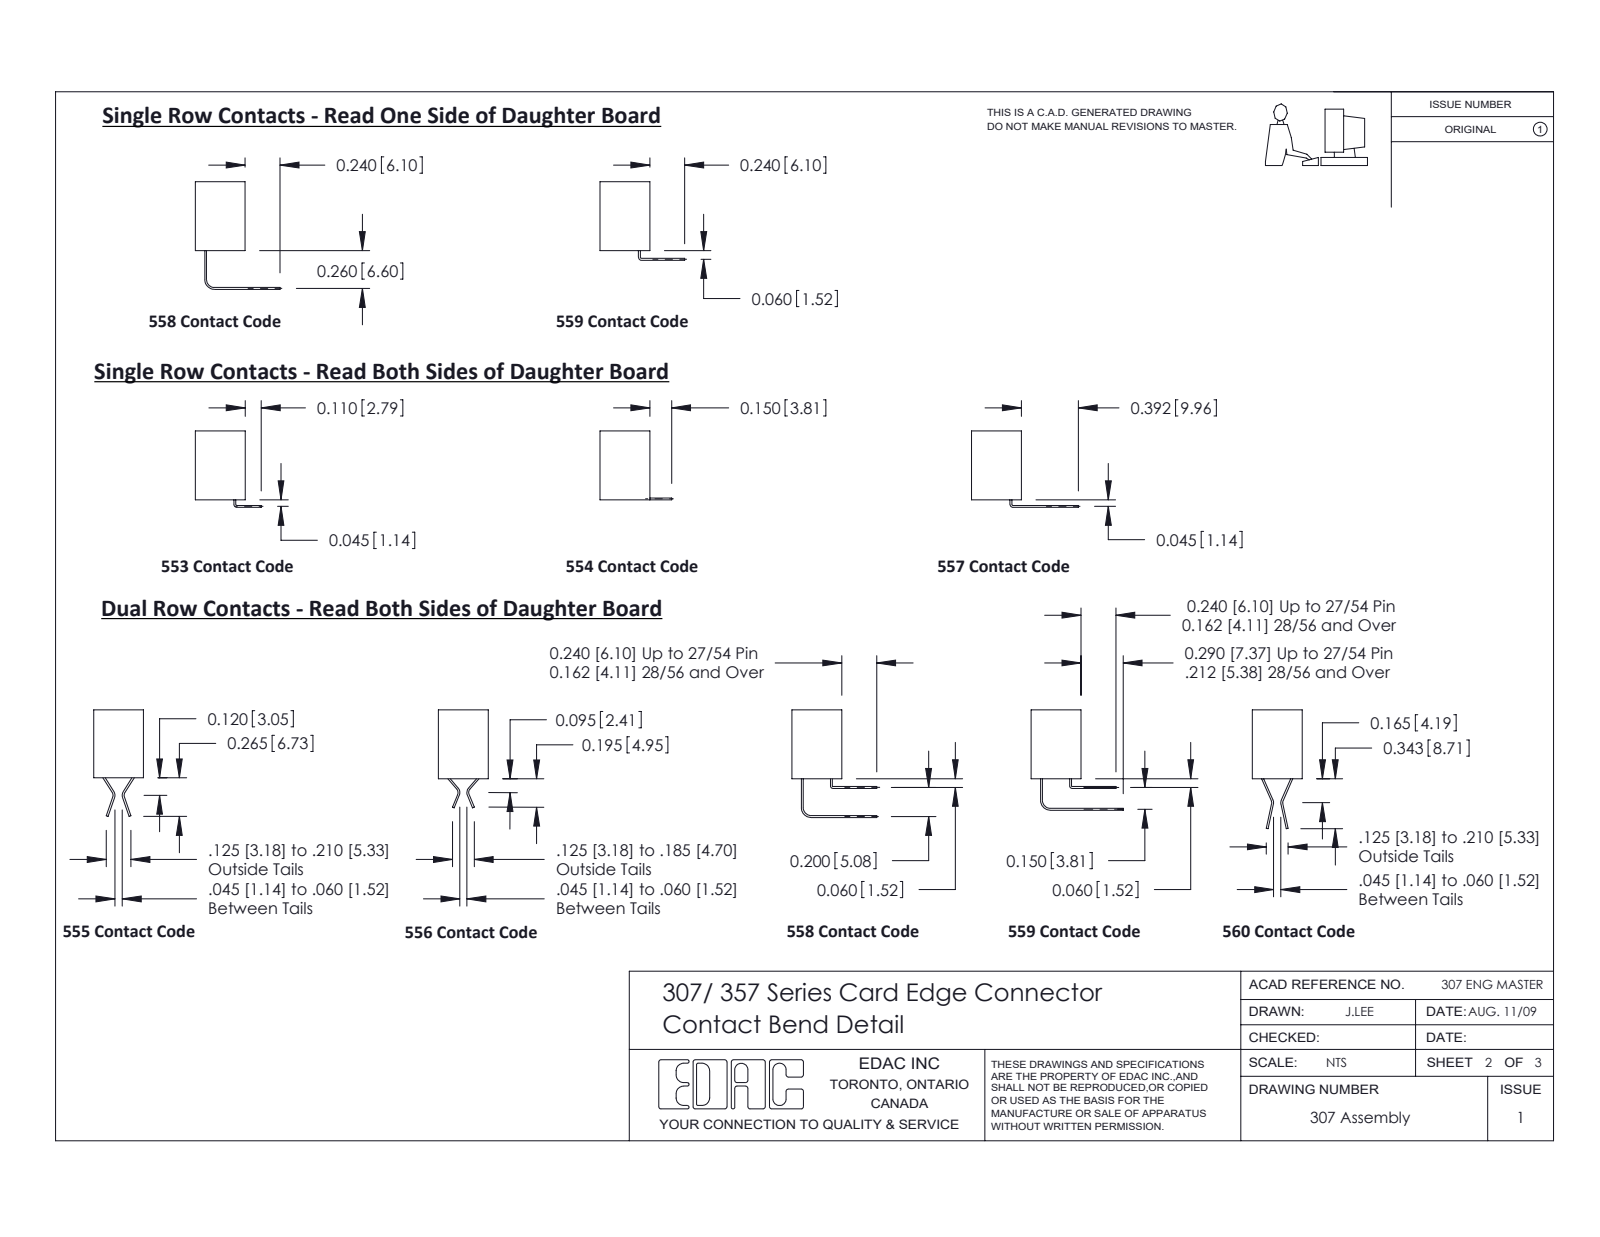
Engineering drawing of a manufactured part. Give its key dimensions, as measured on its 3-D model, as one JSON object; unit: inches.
{"part_name": "307-020-447-101; 307-290-001_547; 307 Part_No Mounting Lugs", "step_written_by": "SolidWorks 2020 (CONFIG_CONTROL_DESIGN)", "units": "inches", "bodies": {"solids": 21, "faces": 1251, "planar": 806, "cylindrical": 403, "other": 42}, "overall_size": [3.43, 1.001, 0.343], "volume_in3": 0.351, "surface_area_in2": 14.61, "partial_cylinders_radius": [[0.02, 106], [0.01, 22], [0.023, 20], [0.007, 6], [0.031, 6], [0.026, 3], [0.046, 2], [0.012, 1]], "face_to_face_distances": [0.065, 0.343, 0.013, 0.278, 0.078, 0.265, 0.064, 0.279, 0.014, 0.215]}
